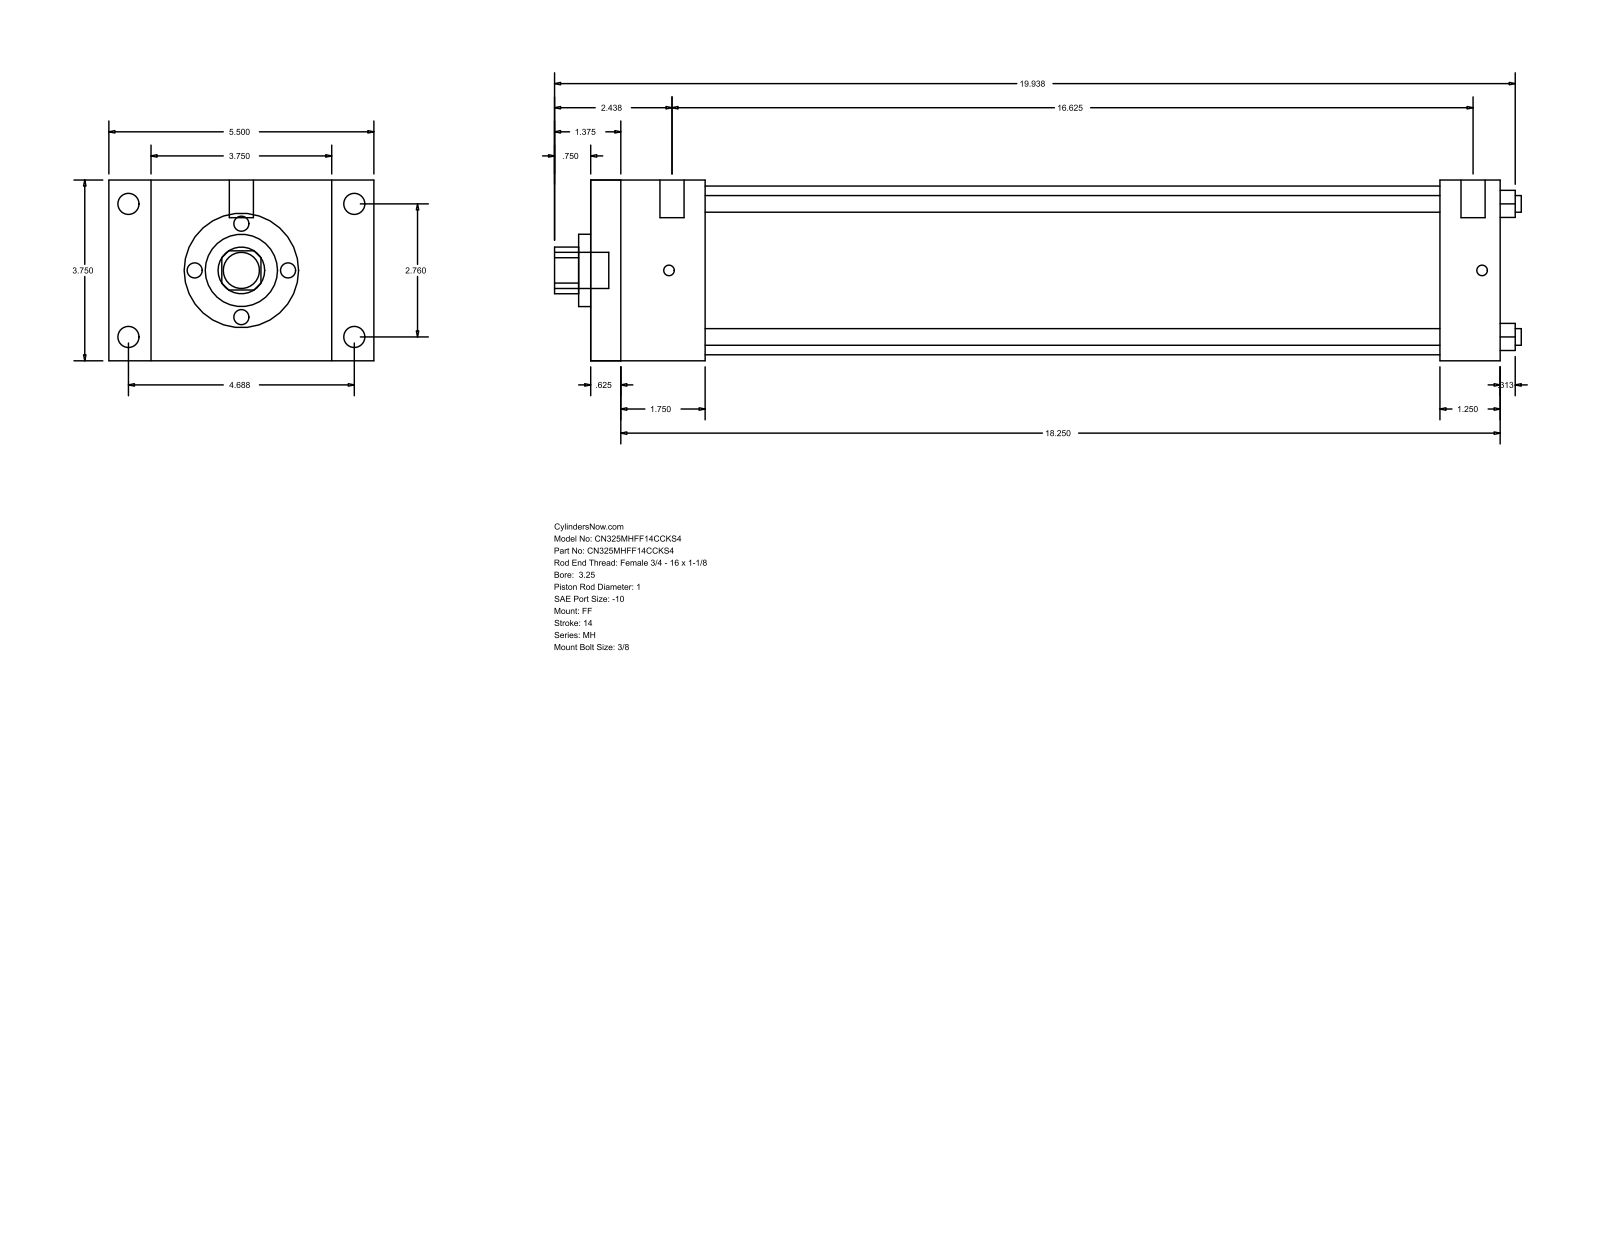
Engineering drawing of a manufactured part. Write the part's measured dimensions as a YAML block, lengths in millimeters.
part_name: "MH_FF__0325_1"
step_written_by: "GSSL Pune (CONFIG_CONTROL_DESIGN)"
units: millimeters
bodies: {solids: 0, faces: 92, planar: 64, cylindrical: 28, other: 0}
overall_size: [509.59, 139.7, 95.25]
round_holes:
  - {diameter: 8.76, count: 4}
  - {diameter: 25.4, count: 1}
  - {diameter: 38.1, count: 1}
  - {diameter: 88.9, count: 1}
round_bosses_or_shafts:
  - {diameter: 11.13, count: 4}
  - {diameter: 5.56, count: 4}
  - {diameter: 12.7, count: 2}
  - {diameter: 19.05, count: 1}
partial_cylinders:
  - {radius: 12.29, count: 1}
face_to_face_distances: [95.24, 479.43, 15.87, 463.56, 22.23, 117.47, 447.68, 431.81, 31.75, 60.33]
hole_center_spacings: [49.57, 70.1, 99.14]
